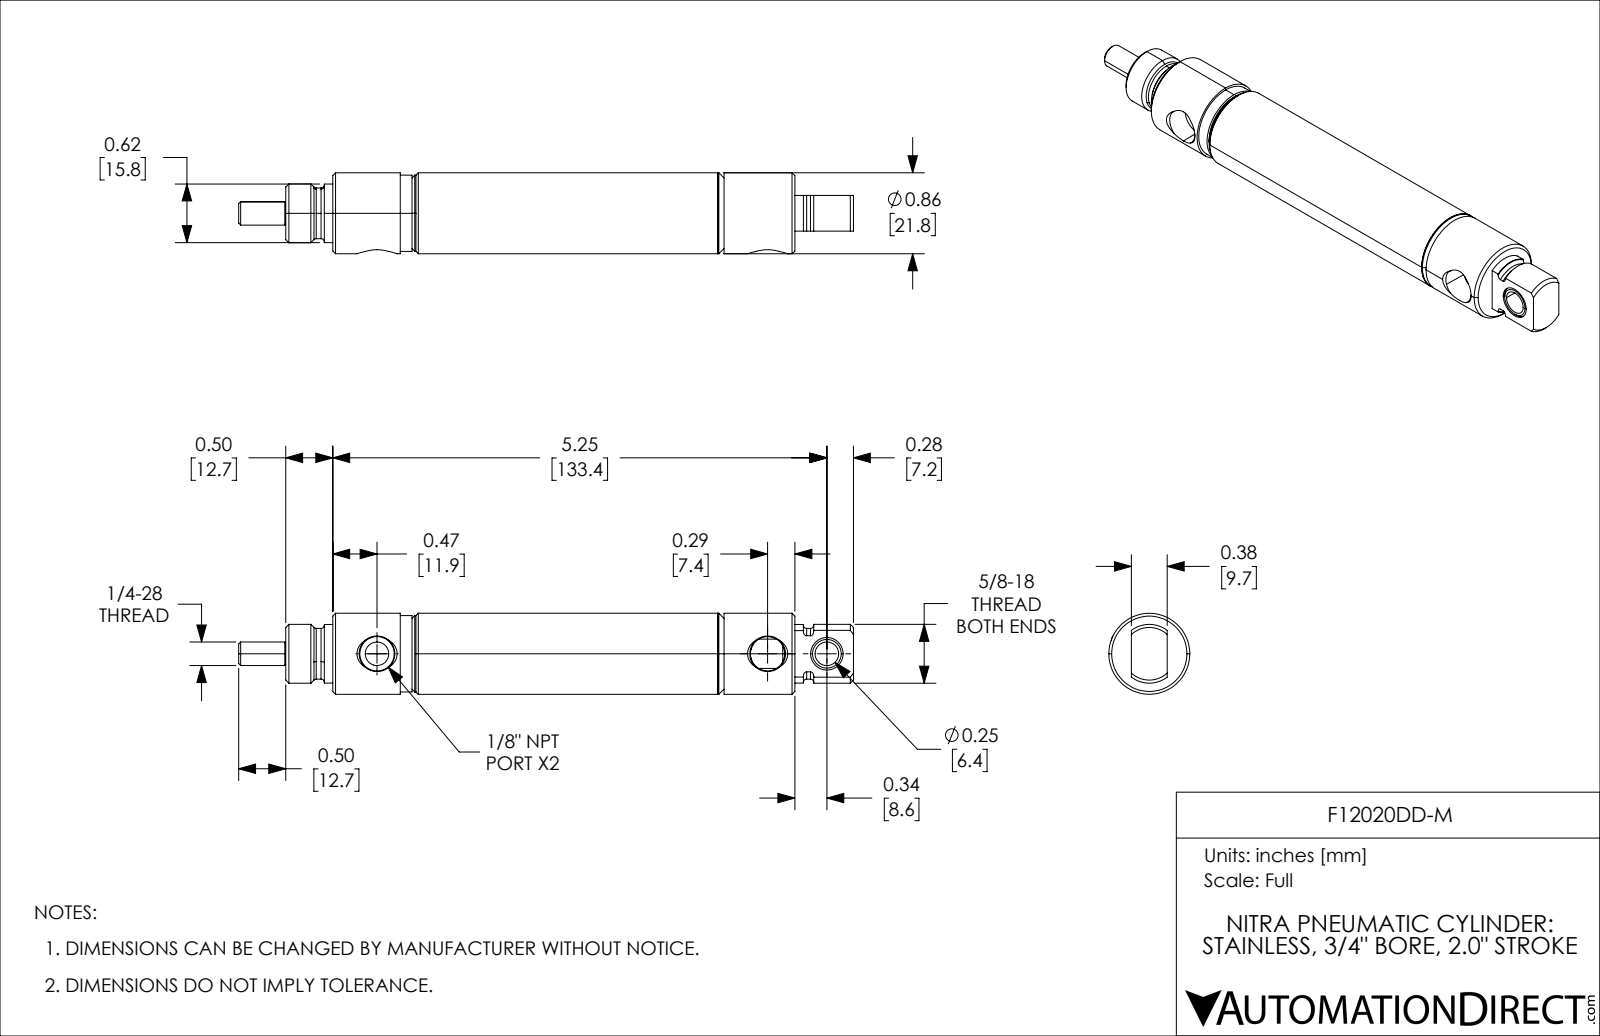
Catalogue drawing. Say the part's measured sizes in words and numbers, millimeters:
The part is named "F12020DD-M_11; F12020DD-M_3; F12020DD-M_7; F12020DD-M (+2 more)". Its 3-D file was written by "SolidWorks 2021 (CONFIG_CONTROL_DESIGN)". It is 5 solids with 158 faces: 29 planar, 61 cylindrical and 68 other. Overall it measures 165.91 by 21.84 by 21.84 millimeters. Its volume is 34 986 cubic millimeters and its surface area 24 025 square millimeters. Round holes: 1 of diameter 6.35, 1 of diameter 6.38, 1 of diameter 6.95, 1 of diameter 7.92, 1 of diameter 8.78, 1 of diameter 9.23, 1 of diameter 12.7, 1 of diameter 17.83. Round bosses or shafts: 1 of diameter 21.84, 1 of diameter 20.57, 1 of diameter 19.35, 1 of diameter 15.88, 1 of diameter 15.81, 1 of diameter 13.68, 1 of diameter 6.35, 1 of diameter 5.84. Partial cylindrical surfaces (rounded edges, fillets, slot ends): 1 of radius 6.84. The main face-to-face distances are 21.43, 40.49, 112.72, 50.8, 72.23, 96.92, 46.12, 24.69, 12.7, 9.66. The hole center spacings are 16, 105.41, 121.41.
